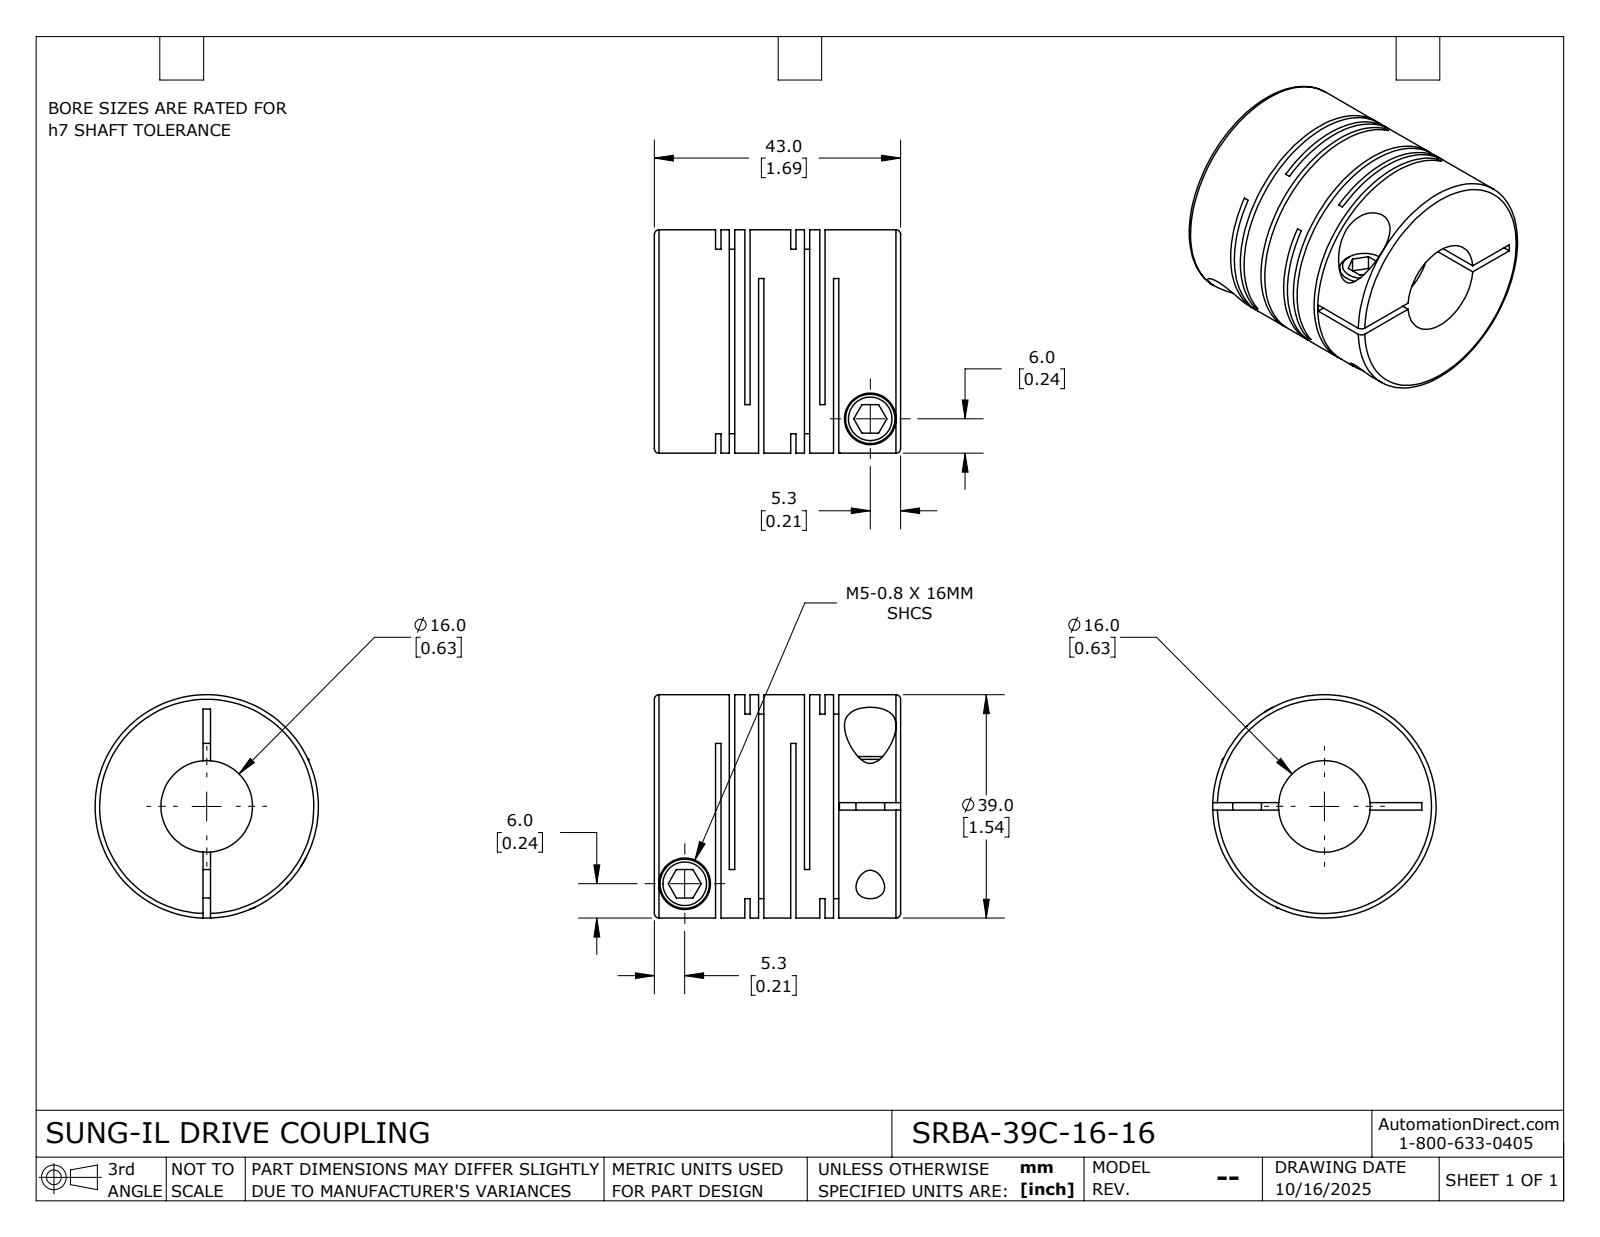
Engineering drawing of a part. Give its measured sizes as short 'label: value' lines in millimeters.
name: SRBA-39C-16-16
written by: SolidWorks 2024 (CONFIG_CONTROL_DESIGN)
unit: mm
bodies: 1 solid, 115 faces (60 planar, 42 cylindrical, 13 other)
size: 43 × 39 × 39
volume: 35 363 mm³; area: 22 946 mm²
holes: 2× ⌀5, 2× ⌀9, 1× ⌀16
bosses: 2× ⌀8.6, 1× ⌀39
face distances: 13.1, 0.92, 2.4, 5.1, 10.7, 14.02, 18.2, 12.18, 1.48, 4.18
